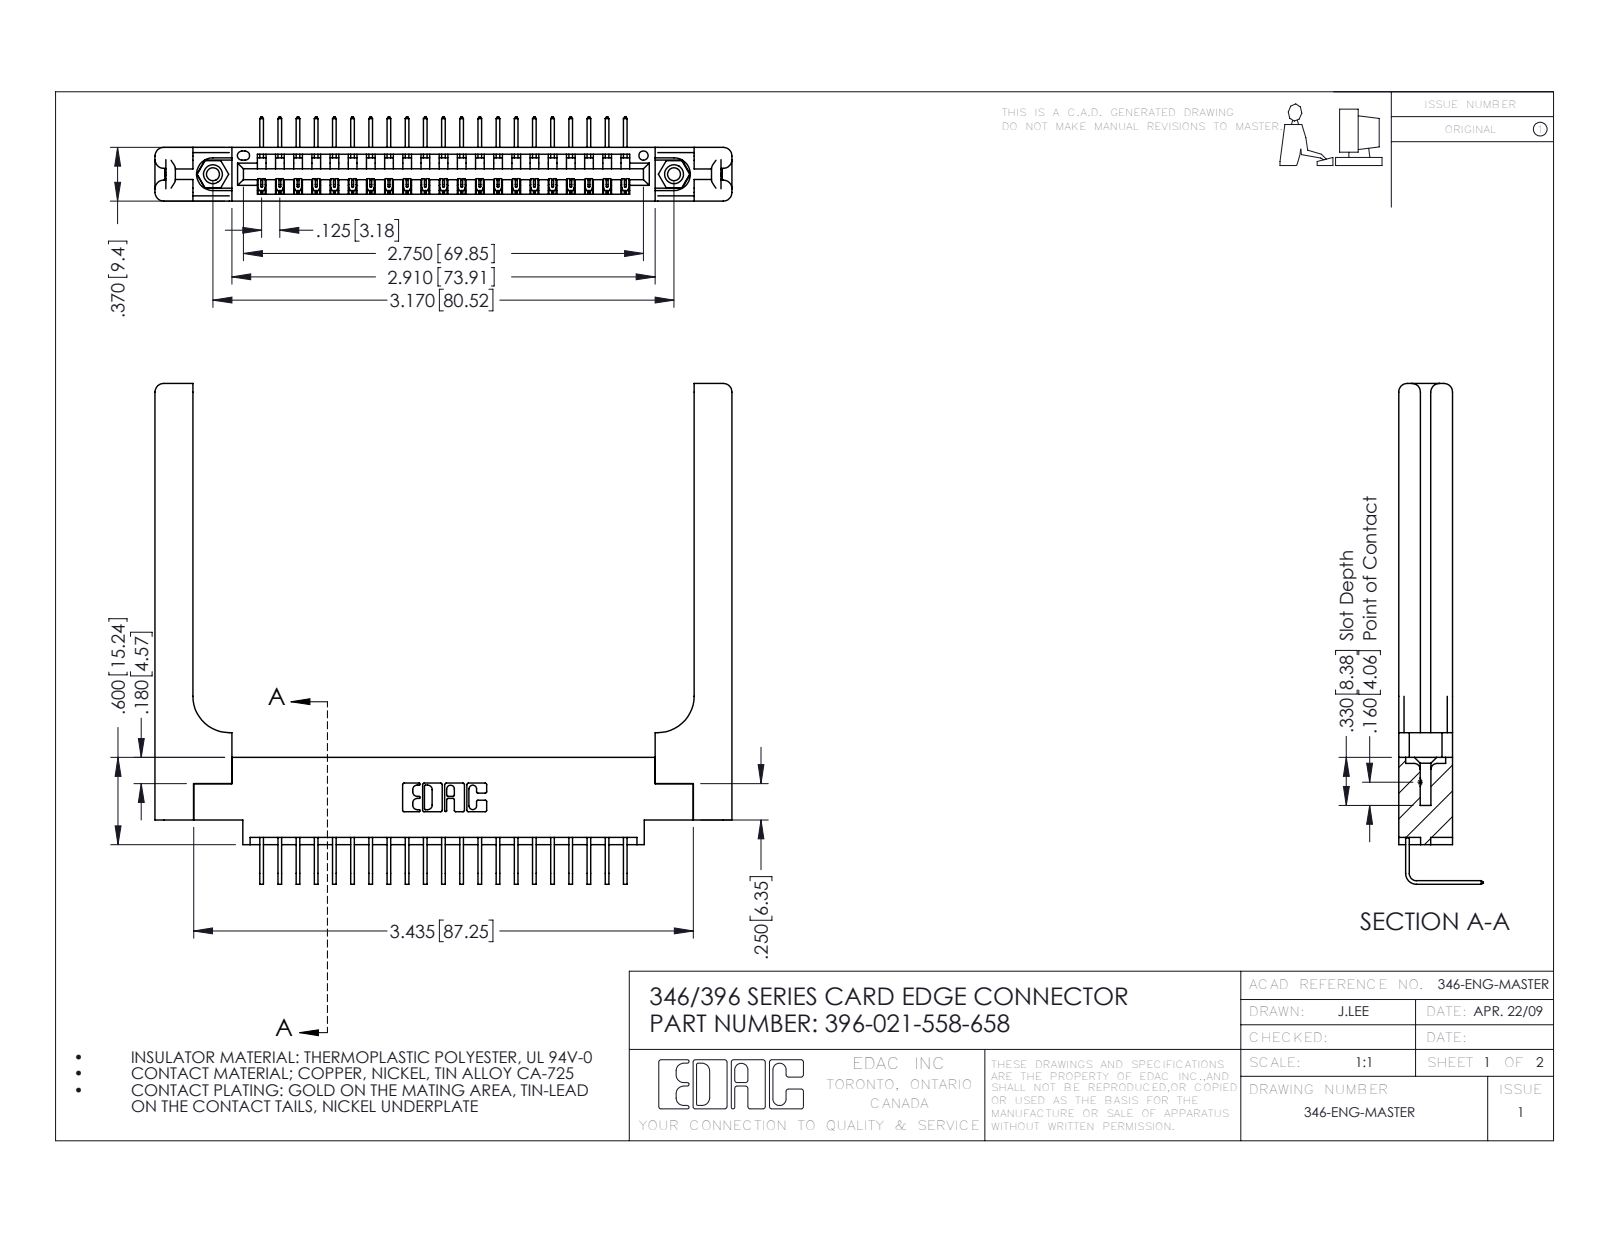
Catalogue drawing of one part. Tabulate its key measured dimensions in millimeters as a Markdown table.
| quantity | value |
| --- | --- |
| part name | 345-292-001_558 Tail - 2; 396-021-558-658; 346 Part_0.170 Offset - 0.156 Dia-TH; 345-250-001_345-250-001-102 (+1 more) |
| STEP written by | SolidWorks 2016 (CONFIG_CONTROL_DESIGN) |
| units | millimeters |
| bodies | 26 solids, 1642 faces (1110 planar, 472 cylindrical, 60 other) |
| overall size | 100.7 × 87.5 × 14.7 |
| volume | 16 930 mm³ |
| surface area | 17 280 mm² |
| round holes (diameter × count) | 2.3 × 2, 3.2 × 2, 4 × 2, 1.6 × 1 |
| round bosses / shafts (diameter × count) | 3.9 × 2 |
| partial cylindrical surfaces (radius × count) | 0.2 × 42, 0.3 × 22, 1.5 × 16, 0.2 × 6, 0.8 × 6, 0.7 × 3, 0.8 × 2, 0.8 × 2 |
| main face-to-face distances | 9.4, 1.8, 8.2, 3.8, 3.8, 1.2, 6.4, 0.6, 7.6, 2.6 |
| hole center spacings | 6.2, 75.3, 80.5 |
